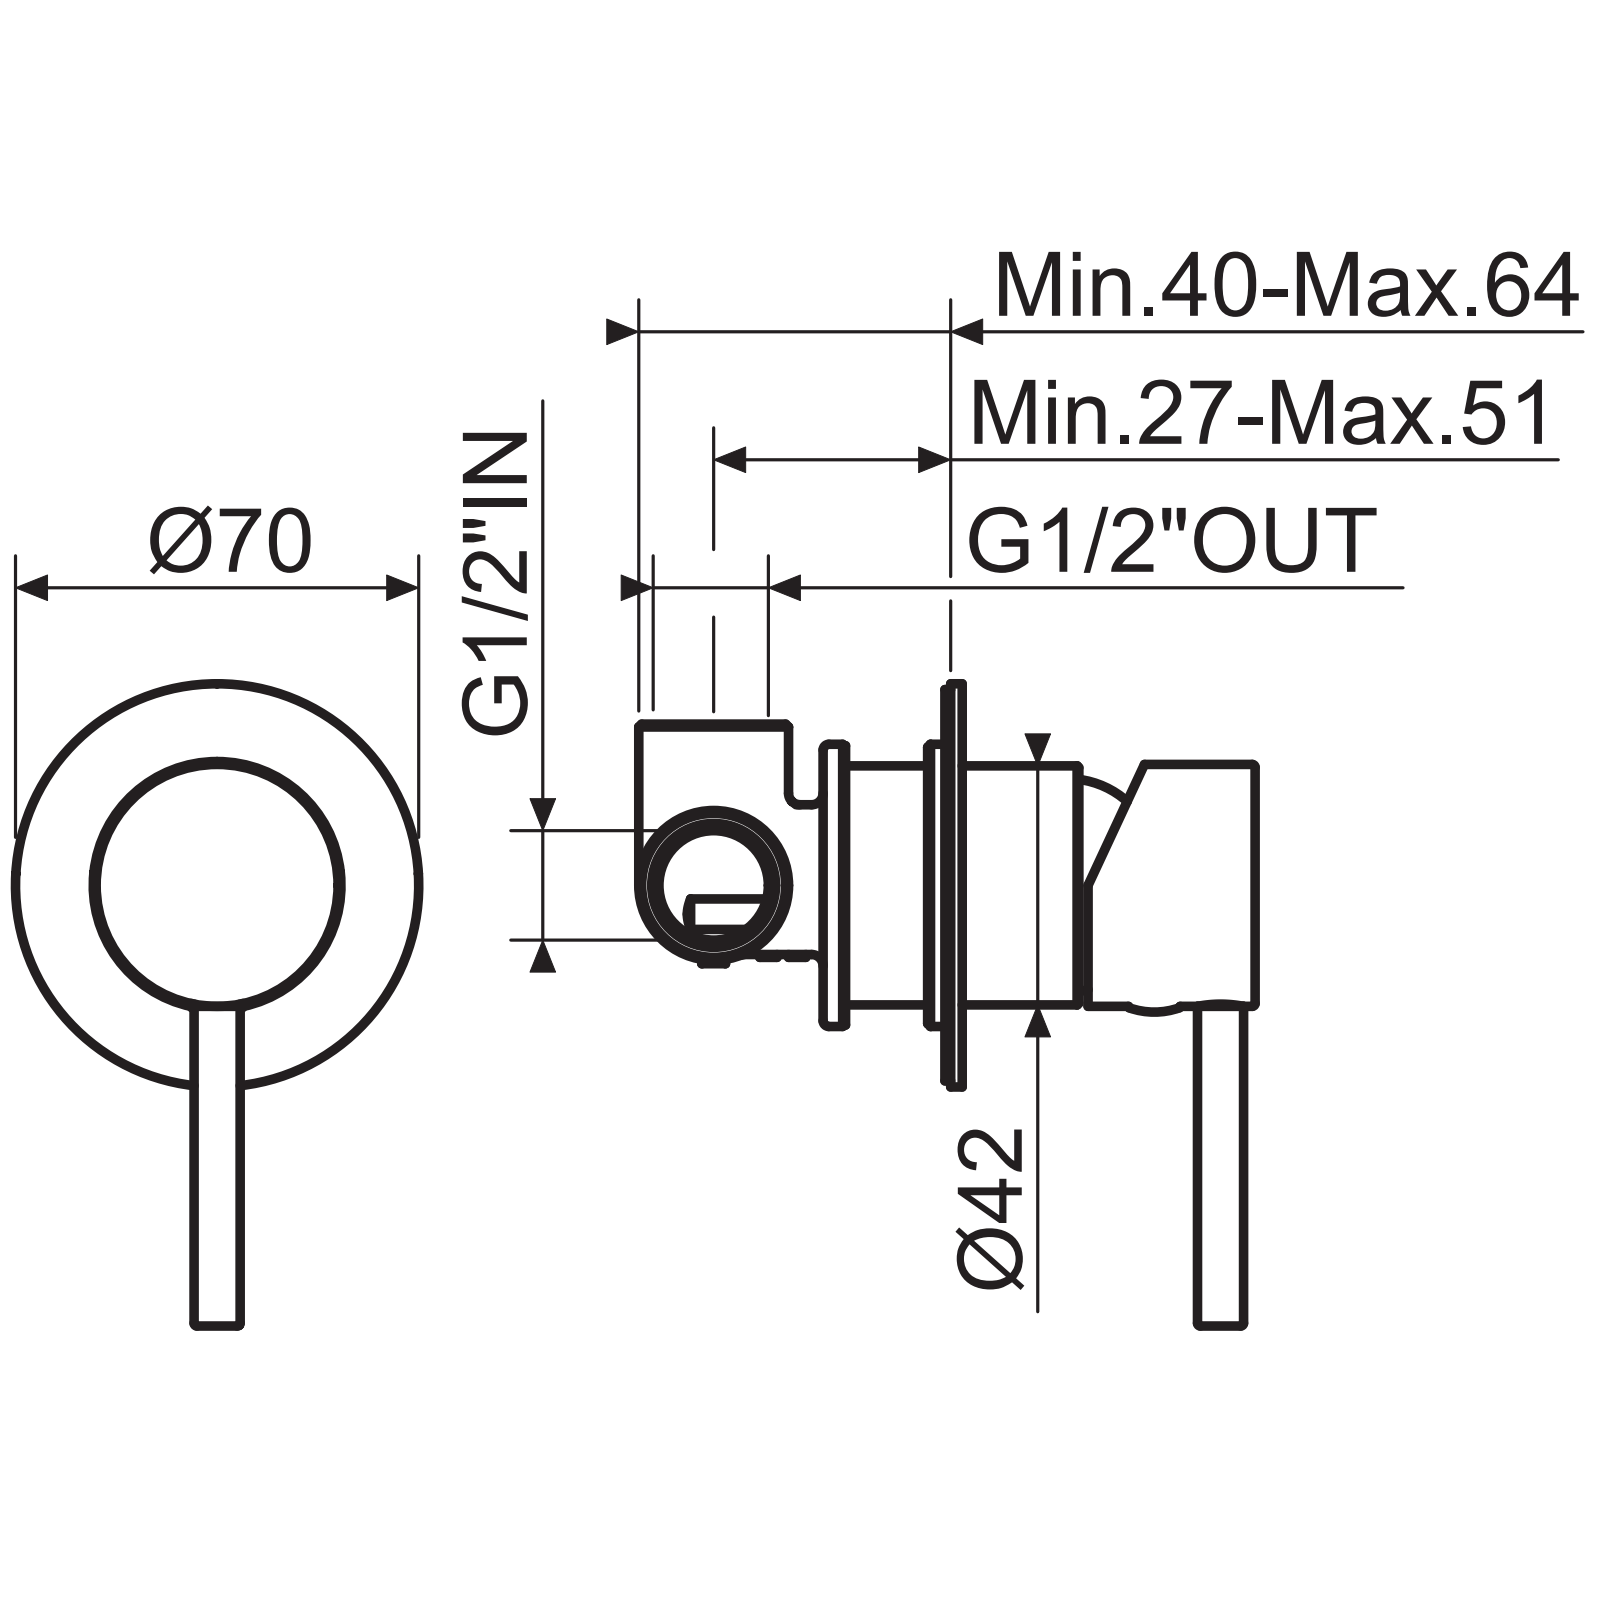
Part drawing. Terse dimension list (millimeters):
name: SINMAC0010_AF1; ALOG230C001; AOTT608C002_AF1; ALOG230W001_AF1 (+8 more)
written by: CREO PARAMETRIC BY PTC INC, 2022164 (CONFIG_CONTROL_DESIGN)
unit: mm
bodies: 10 solids, 295 faces (83 planar, 101 cylindrical, 111 other)
size: 111.5 × 70 × 53.32
volume: 23 123 mm³; area: 32 792 mm²
holes: 3× ⌀8, 2× ⌀4.2, 1× ⌀5, 1× ⌀5.1, 1× ⌀6.5, 1× ⌀27.7, 1× ⌀32, 1× ⌀37.5, 1× ⌀40, 1× ⌀43, 1× ⌀46.5, 1× ⌀50
bosses: 1× ⌀70, 1× ⌀68, 1× ⌀49, 1× ⌀42, 1× ⌀41.5, 1× ⌀36.8, 1× ⌀5
rounds: 14× R1, 11× R0.5, 4× R2, 2× R0.3, 2× R1.5, 2× R2.6, 2× R3, 2× R4.8
face distances: 2, 0.47, 2.47, 50.85, 53.32, 52.85, 48.85, 51.32, 4, 49.32
hole spacings: 11.5
